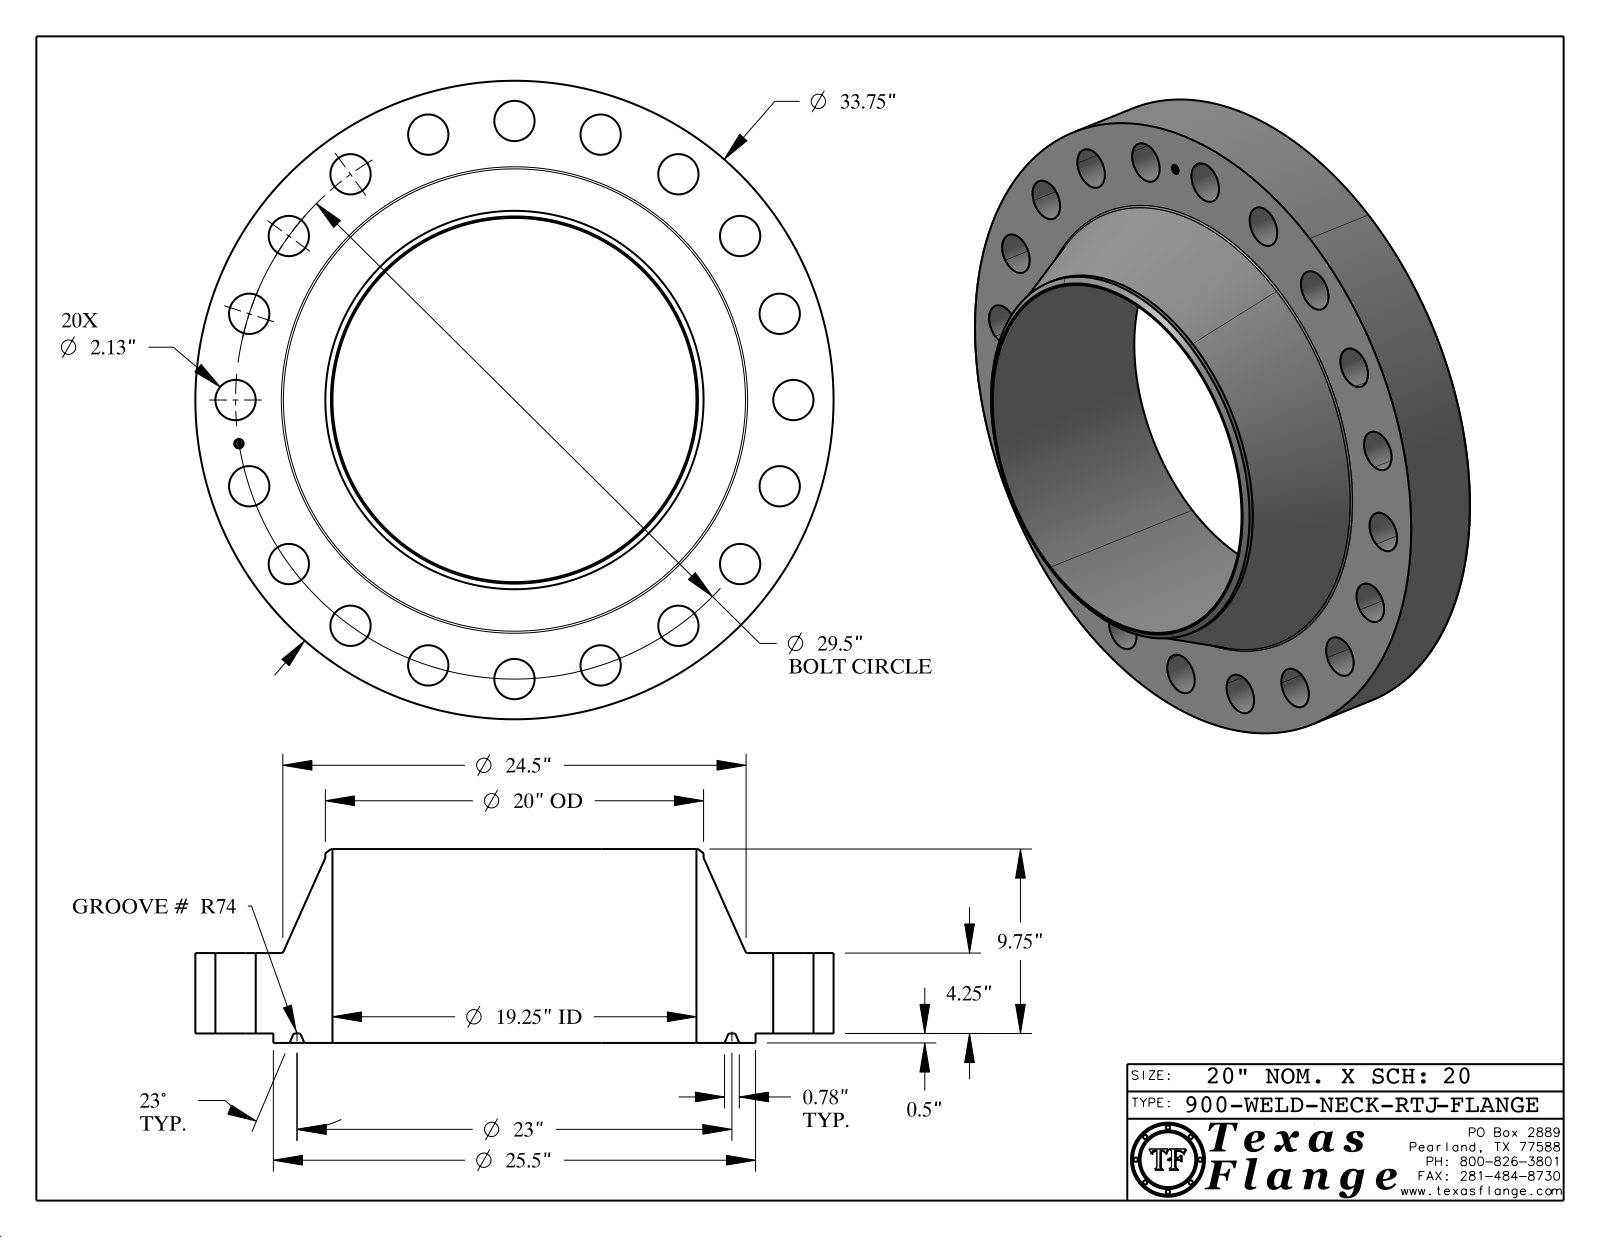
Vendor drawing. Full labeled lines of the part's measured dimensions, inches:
Part name (STEP PRODUCT): 900-WELD-NECK-RTJ
STEP written by: CATIA V5 STEP AP214 (AUTOMOTIVE_DESIGN)
Units: inches
Bodies: 1 solid, 453 faces (371 planar, 68 cylindrical, 14 other)
Overall size (bounding box): 33.75 × 33.75 × 10.25
Volume: 2 859 in³ · Surface area: 3 037 in²
Round holes (diameter × count): ⌀2.13 ×20, ⌀0.495 ×1, ⌀19.25 ×1
Round bosses / shafts (diameter × count): ⌀0.03 ×8, ⌀33.75 ×1, ⌀25.5 ×1, ⌀20 ×1, ⌀0.39 ×1
Main face-to-face distances: 4.25, 0.5, 4.75, 10.25, 9.75, 5.5, 4.735, 4.235, 0.015, 5.515
Hole centre spacings: 14.75, 29.137, 4.615, 17.34, 20.859, 23.866, 26.285, 9.116
